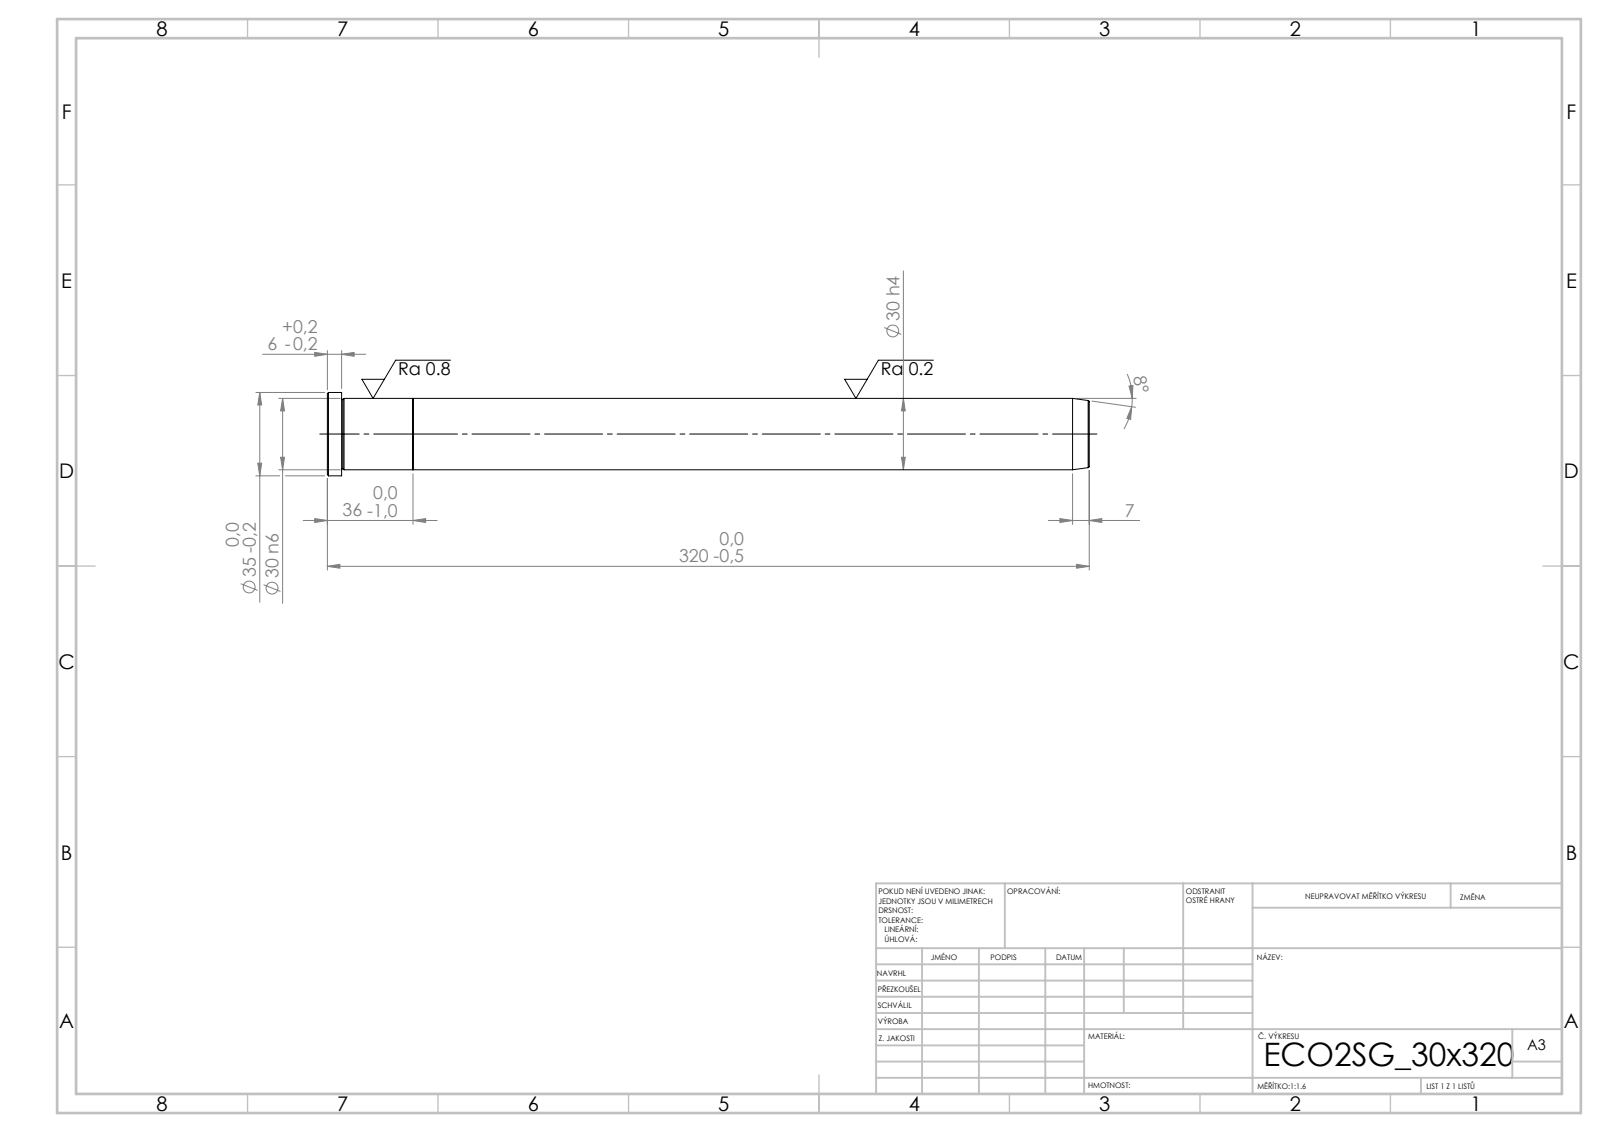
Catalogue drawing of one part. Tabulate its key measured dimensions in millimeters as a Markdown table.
| quantity | value |
| --- | --- |
| STEP written by | SolidWorks 2019 (CONFIG_CONTROL_DESIGN) |
| units | millimeters |
| bodies | 2 solids, 21 faces (5 planar, 6 cylindrical, 10 other) |
| overall size | 320 × 35 × 35 |
| volume | 227 355 mm³ |
| surface area | 33 491 mm² |
| round bosses / shafts (diameter × count) | 35 × 1, 30 × 1 |
| main face-to-face distances | 36, 284, 320, 314, 30, 6 |
